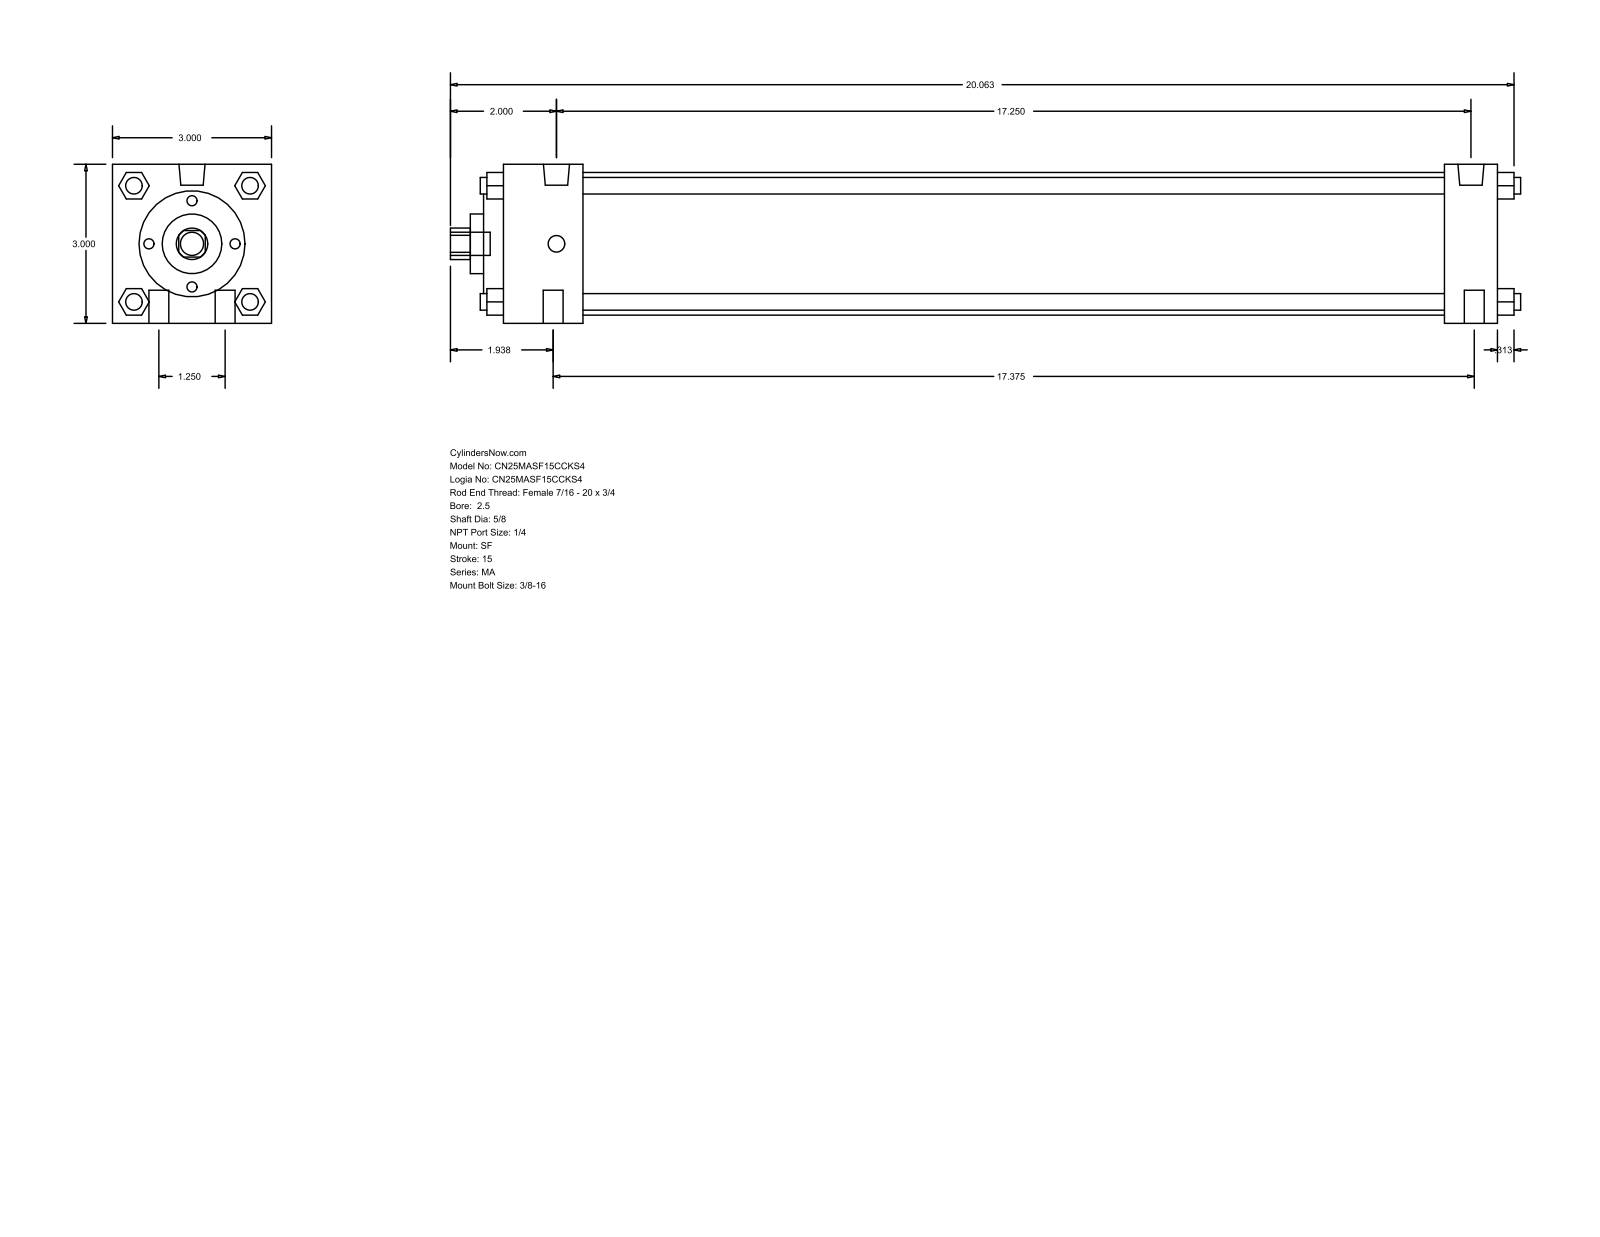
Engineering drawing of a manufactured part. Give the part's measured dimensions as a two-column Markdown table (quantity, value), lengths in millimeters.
| quantity | value |
| --- | --- |
| part name | MA_SF__0250_0.625 |
| STEP written by | GSSL Pune (CONFIG_CONTROL_DESIGN) |
| units | millimeters |
| bodies | 0 solids, 126 faces (95 planar, 31 cylindrical, 0 other) |
| overall size | 512.76 × 76.2 × 76.2 |
| round holes (diameter × count) | 15.88 × 1, 28.57 × 1, 50.8 × 1, 68.33 × 1 |
| round bosses / shafts (diameter × count) | 7.94 × 6, 9.53 × 4, 12.49 × 2, 11.11 × 1 |
| partial cylindrical surfaces (radius × count) | 7.54 × 1 |
| main face-to-face distances | 76.2, 476.25, 25.4, 450.85, 38.1, 412.75, 438.15, 12.7, 9.52, 47.62 |
